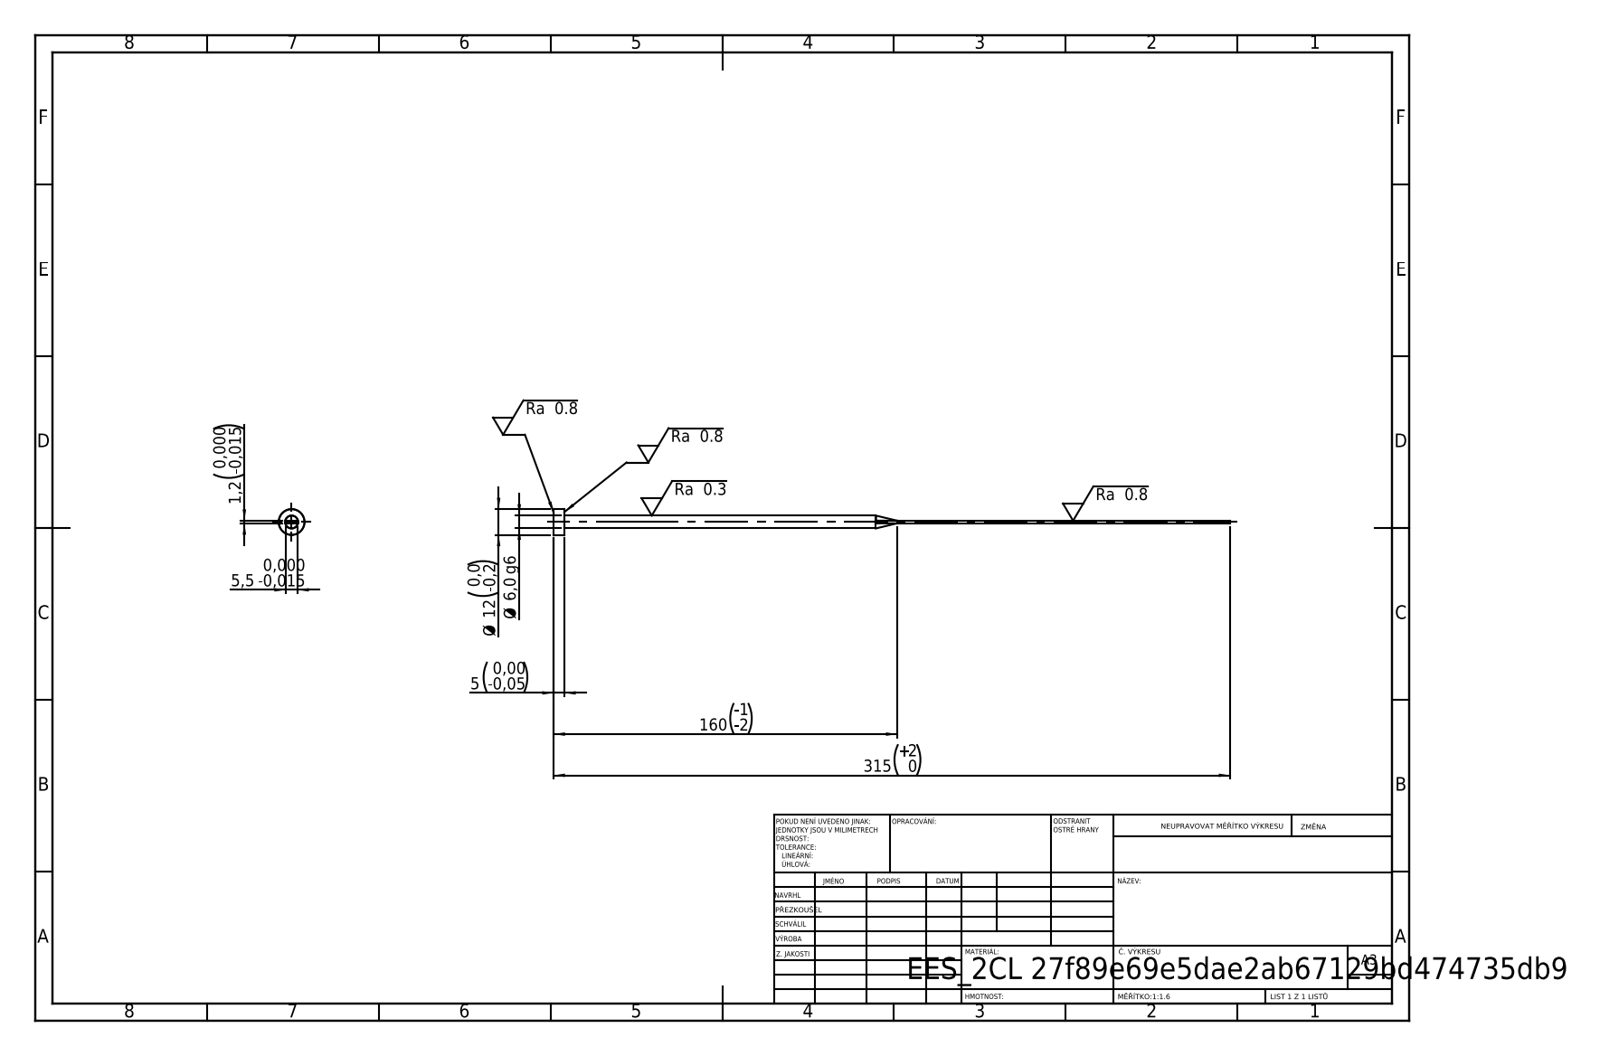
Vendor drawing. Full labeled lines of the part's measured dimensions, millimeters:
STEP written by: SolidWorks 2019 (CONFIG_CONTROL_DESIGN)
Units: millimetres
Bodies: 1 solid, 15 faces (7 planar, 4 cylindrical, 4 other)
Overall size (bounding box): 315 × 12 × 12
Volume: 5 854 mm³ · Surface area: 5 359 mm²
Round bosses / shafts (diameter × count): ⌀12 ×1, ⌀6 ×1
Main face-to-face distances: 1.2, 5.5, 5, 315, 310
